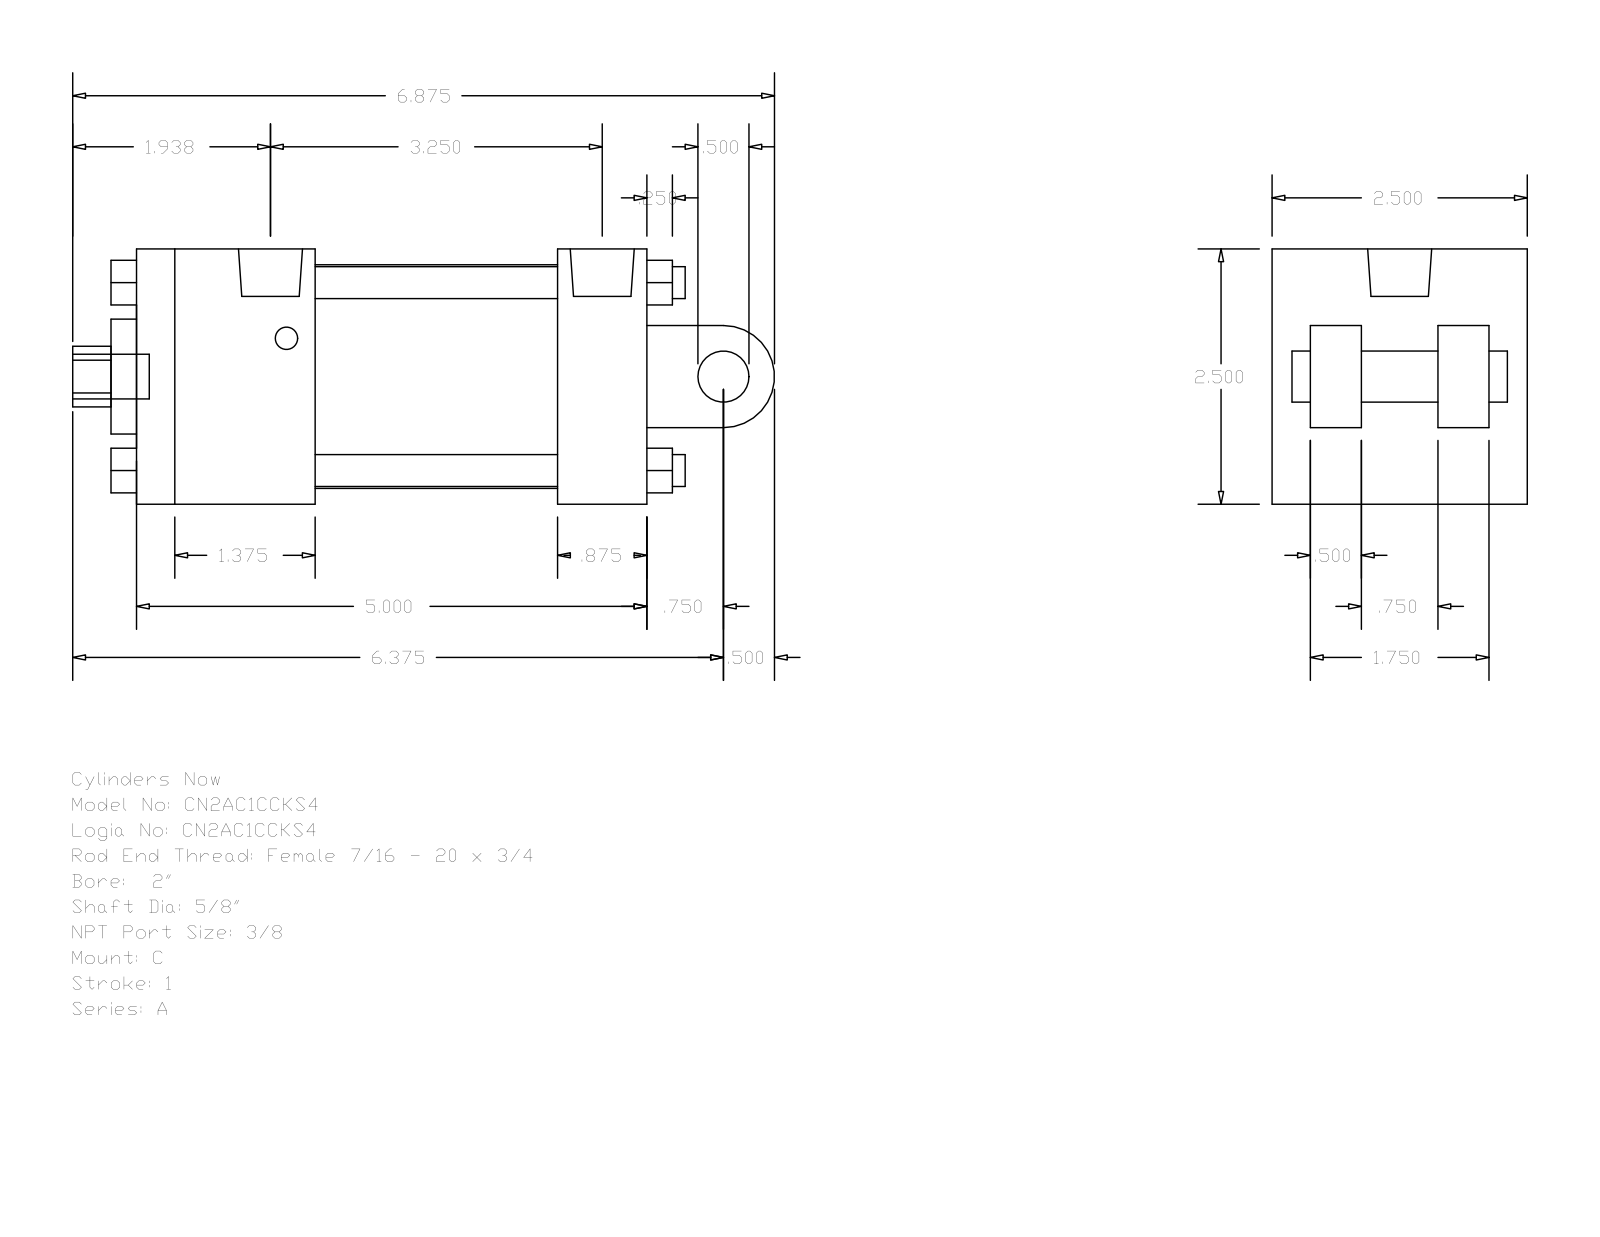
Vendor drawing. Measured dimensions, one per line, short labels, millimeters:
name: A_C__0200_0.625
written by: GSSL Pune (CONFIG_CONTROL_DESIGN)
unit: mm
bodies: 0 solids, 135 faces (102 planar, 33 cylindrical, 0 other)
size: 174.62 × 63.5 × 63.5
holes: 2× ⌀5.56, 1× ⌀15.88, 1× ⌀15.93, 1× ⌀28.57, 1× ⌀55.63
bosses: 4× ⌀7.94, 2× ⌀5.56, 1× ⌀15.93, 1× ⌀12.7, 1× ⌀11.11
rounds: 1× R7.54, 1× R12.7
face distances: 63.5, 127, 44.45, 9.52, 82.55, 104.77, 60.32, 22.23, 12.7, 41.28
hole spacings: 3.97
